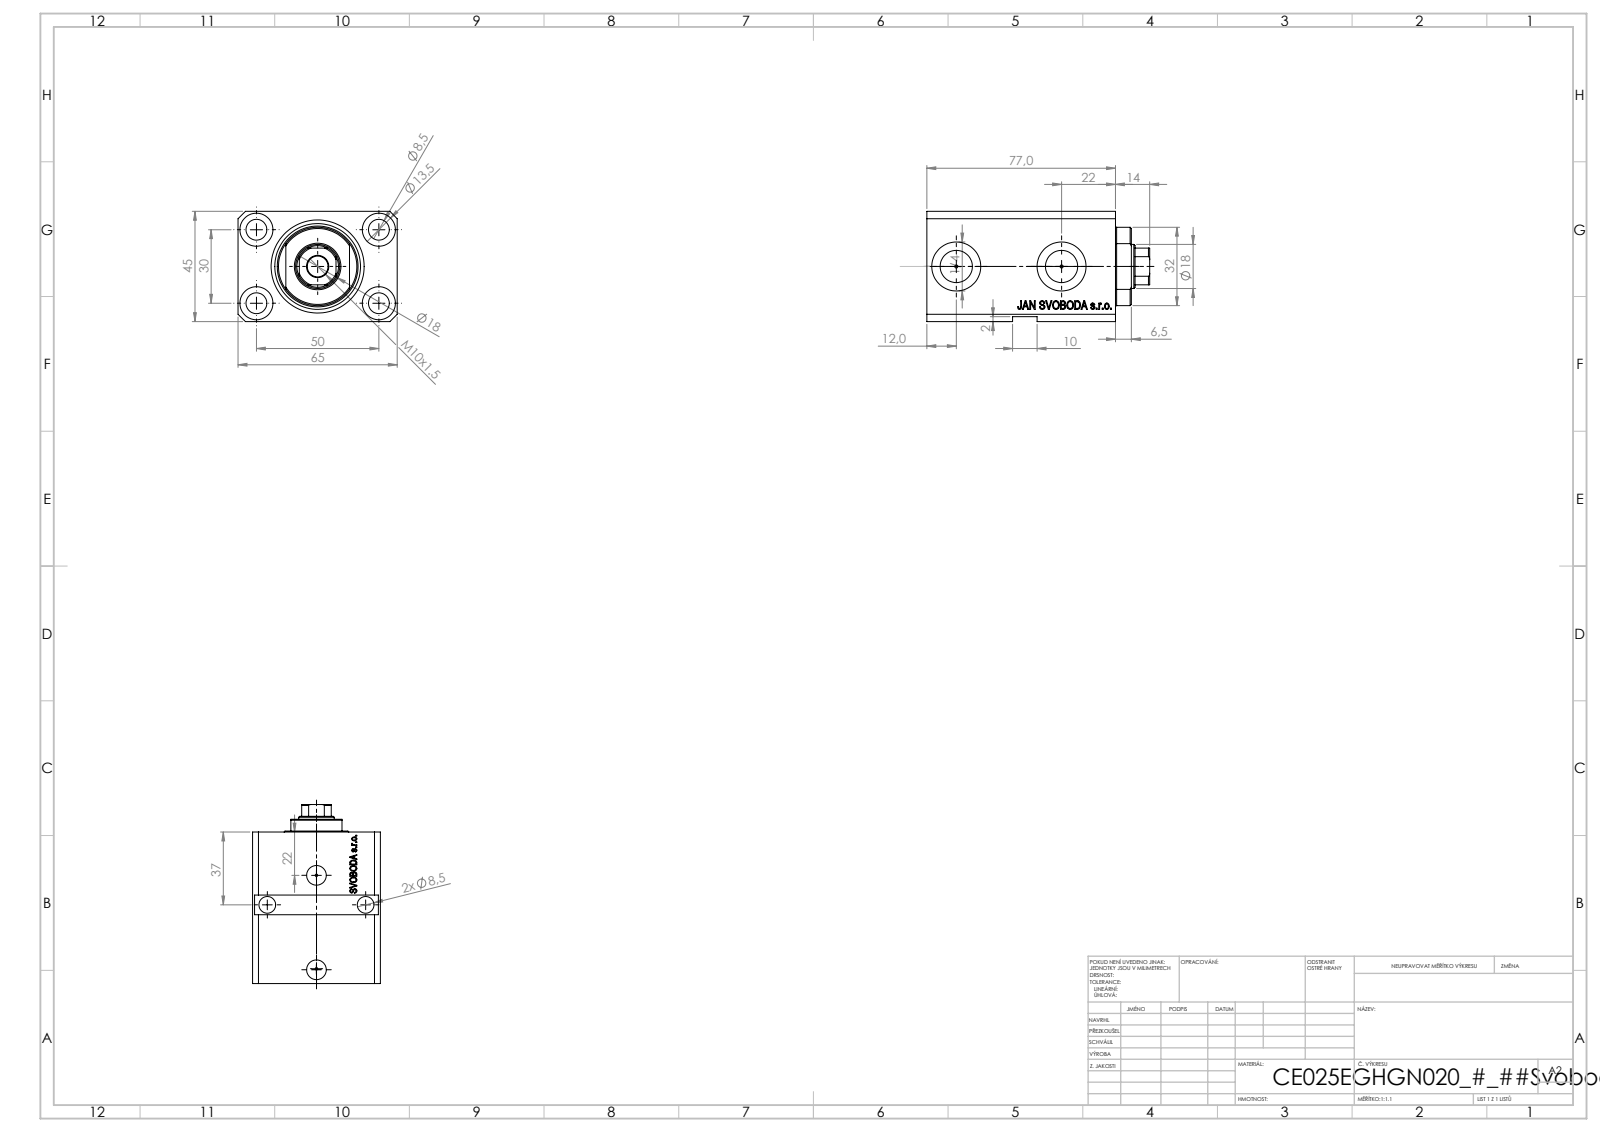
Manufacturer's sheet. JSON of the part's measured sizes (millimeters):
{"part_name": "V250CE_E_Body; V250CE_C_VCP; V250CE_VC_E", "step_written_by": "SolidWorks 2019 (CONFIG_CONTROL_DESIGN)", "units": "millimeters", "bodies": {"solids": 3, "faces": 897, "planar": 435, "cylindrical": 84, "other": 378}, "overall_size": [91, 65, 45], "volume_mm3": 191714, "surface_area_mm2": 52259, "round_holes": [[8.5, 7], [1.25, 4], [13.5, 4], [10, 2], [13.16, 2], [20, 2], [18, 1], [25, 1], [38, 1]], "partial_cylinders_radius": [[8.5, 1], [16, 1]], "face_to_face_distances": [45, 65, 63, 14, 77, 6.9, 56.1, 70.1, 43, 9], "hole_center_spacings": [29.15, 50, 30, 40.98, 41.4, 58.31, 0.53, 43]}
